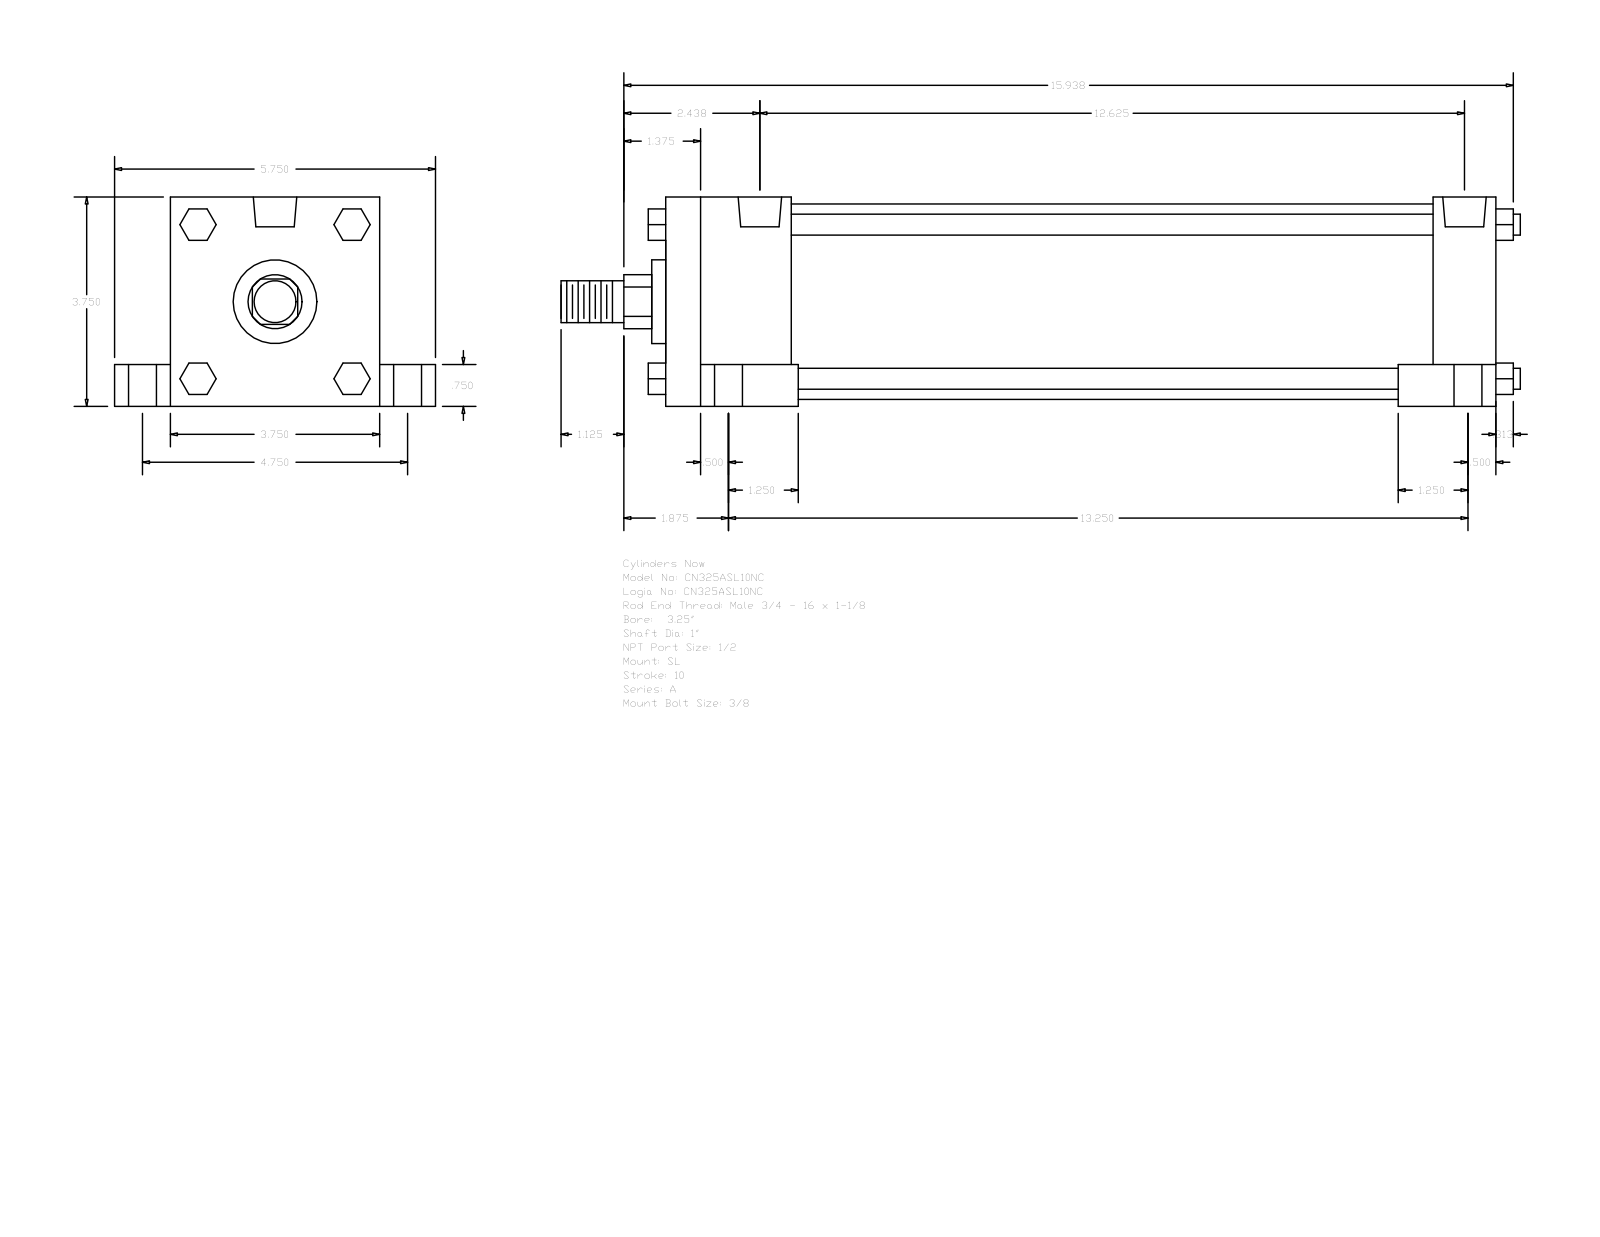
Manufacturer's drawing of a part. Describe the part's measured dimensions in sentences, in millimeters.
The part is named "A_SL__0325_1". Its 3-D file was written by "GSSL Pune (CONFIG_CONTROL_DESIGN)". It is 0 solids with 150 faces: 114 planar, 36 cylindrical and 0 other. Overall it measures 436.56 by 146.05 by 95.25 millimeters. Round holes: 4 of diameter 8.73, 4 of diameter 12.7, 4 of diameter 19.05, 2 of diameter 19.77. Round bosses or shafts: 4 of diameter 9.53, 1 of diameter 88.9, 1 of diameter 38.1, 1 of diameter 25.4, 1 of diameter 19.05. Partial cylindrical surfaces (rounded edges, fillets, slot ends): 1 of radius 12.29. The main face-to-face distances are 95.24, 377.83, 19.05, 25.41, 120.65, 76.19, 57.15, 349.25, 292.1, 320.68. The hole center spacings are 3.18, 60.35, 60.52, 62, 62.81, 120.66, 314.32, 317.5.
